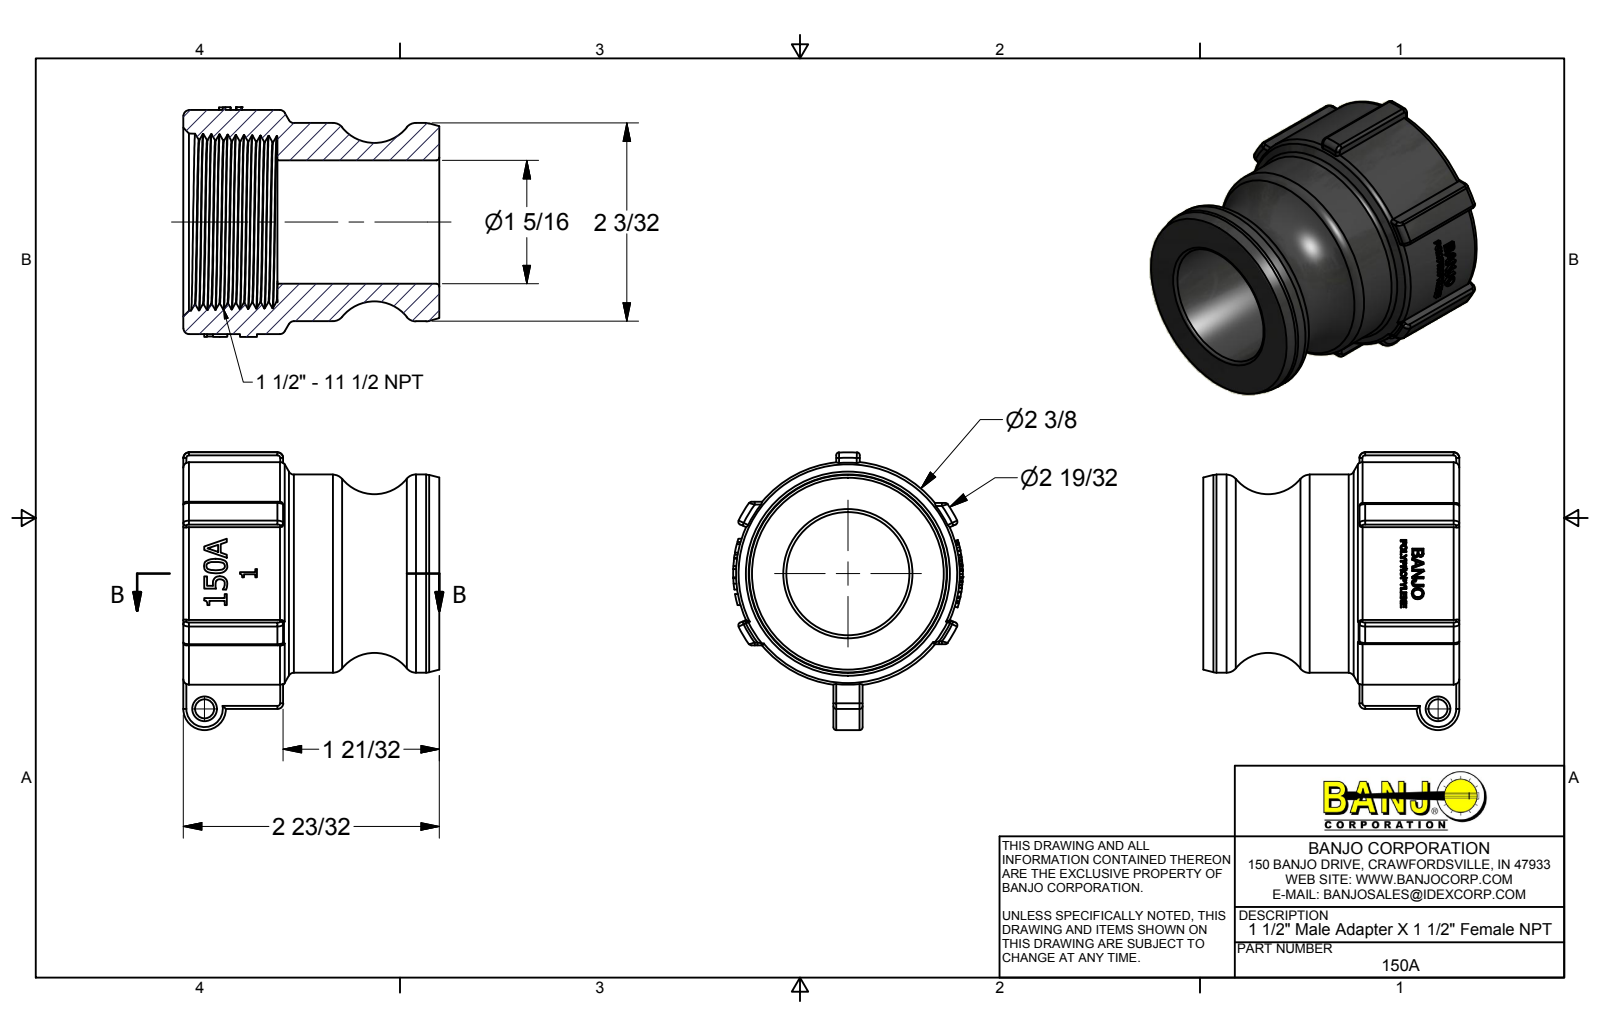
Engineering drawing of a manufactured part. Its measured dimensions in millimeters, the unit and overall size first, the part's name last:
Units: millimetres
Overall size (bounding box): 74.98 × 69.09 × 61.98
Round holes (diameter × count): ⌀5.08 ×1, ⌀33.27 ×1
Round bosses / shafts (diameter × count): ⌀53.47 ×1
Partial cylindrical surfaces — rounded edges, fillets, slot ends (radius × count): R0.79 ×36, R1.52 ×1, R5.71 ×1, R13.56 ×1, R30.23 ×1, R30.99 ×1, R32.77 ×1
Main face-to-face distances: 43.69, 69.09, 25.4, 7.88, 0.33, 38.43, 0.77, 7.11, 17.12, 55.88
Volume: 85 076 mm³ · Surface area: 27 783 mm²
Bodies: 1 solid, 480 faces (176 planar, 89 cylindrical, 215 other)
Part name (STEP PRODUCT): 150A
STEP written by: Autodesk Inventor 2014 (AUTOMOTIVE_DESIGN)
